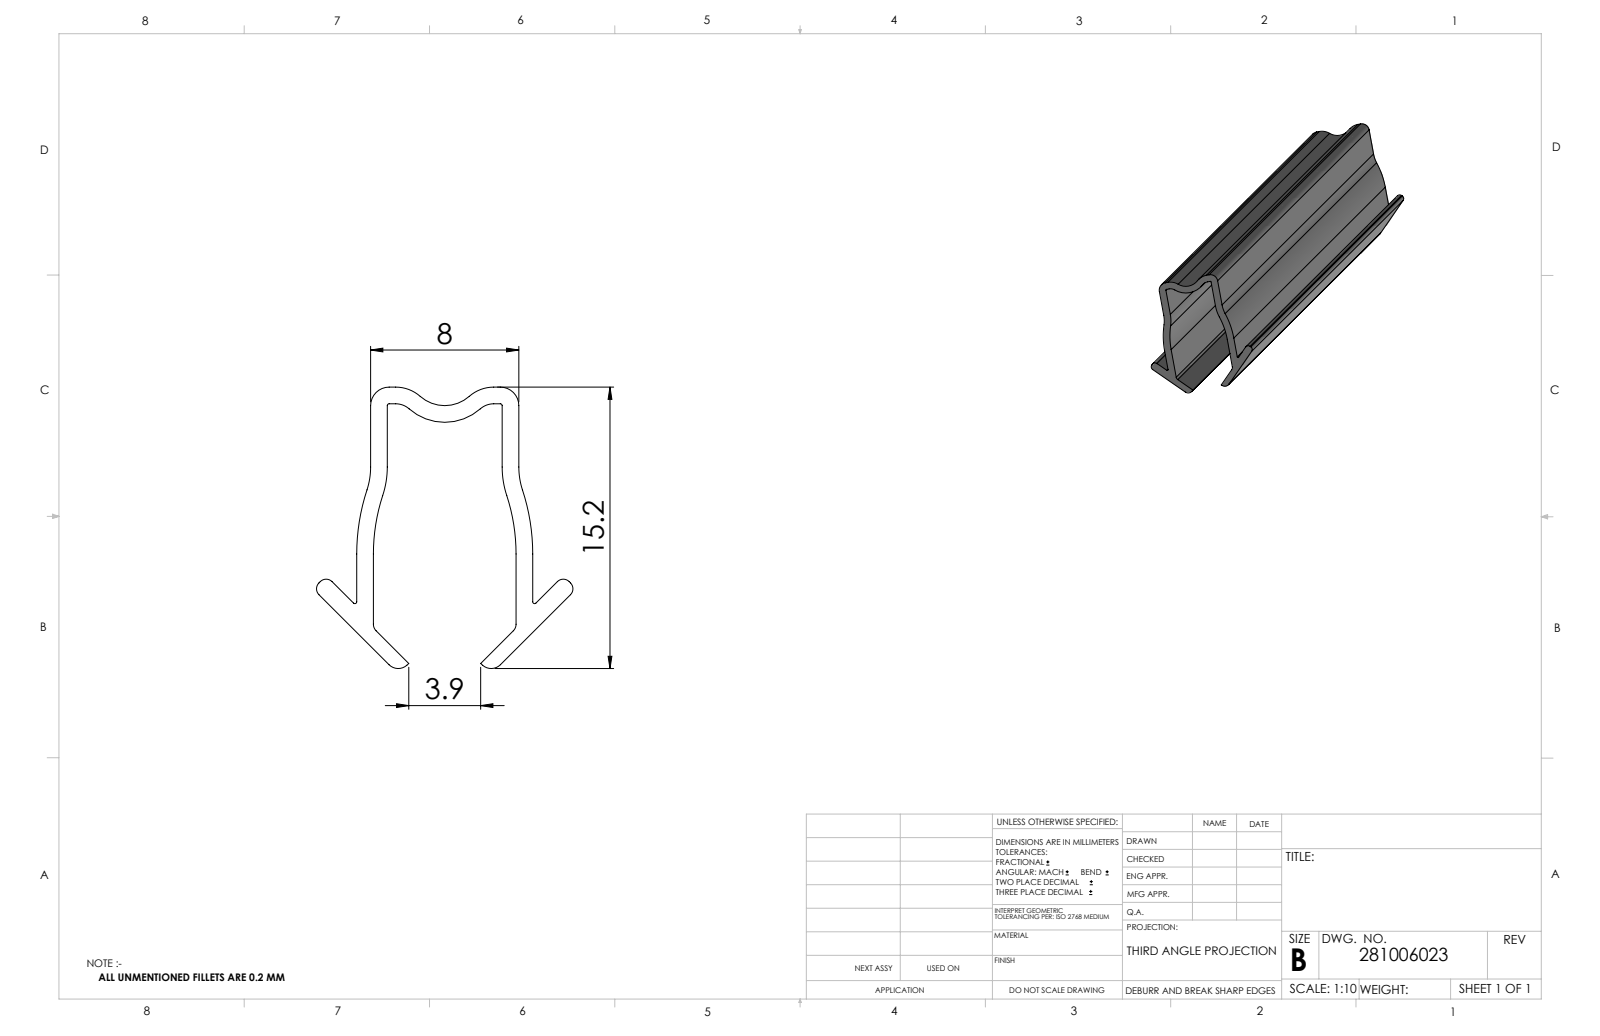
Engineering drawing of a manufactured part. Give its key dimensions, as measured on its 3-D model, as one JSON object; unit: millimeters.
{"part_name": "281006023_c_1", "step_written_by": "SolidWorks 2014 (CONFIG_CONTROL_DESIGN)", "units": "millimeters", "bodies": {"solids": 1, "faces": 53, "planar": 24, "cylindrical": 29, "other": 0}, "overall_size": [1000, 15.18, 13.84], "volume_mm3": 39350, "surface_area_mm2": 87218, "partial_cylinders_radius": [[0.1, 4], [0.45, 4], [2, 3], [0.5, 2], [0.7, 2], [1, 2], [1.1, 2], [4, 2]], "face_to_face_distances": [0.9, 0.75, 7.85, 6.95, 7.1, 1.65, 8.6, 8.75, 7.7, 8]}
